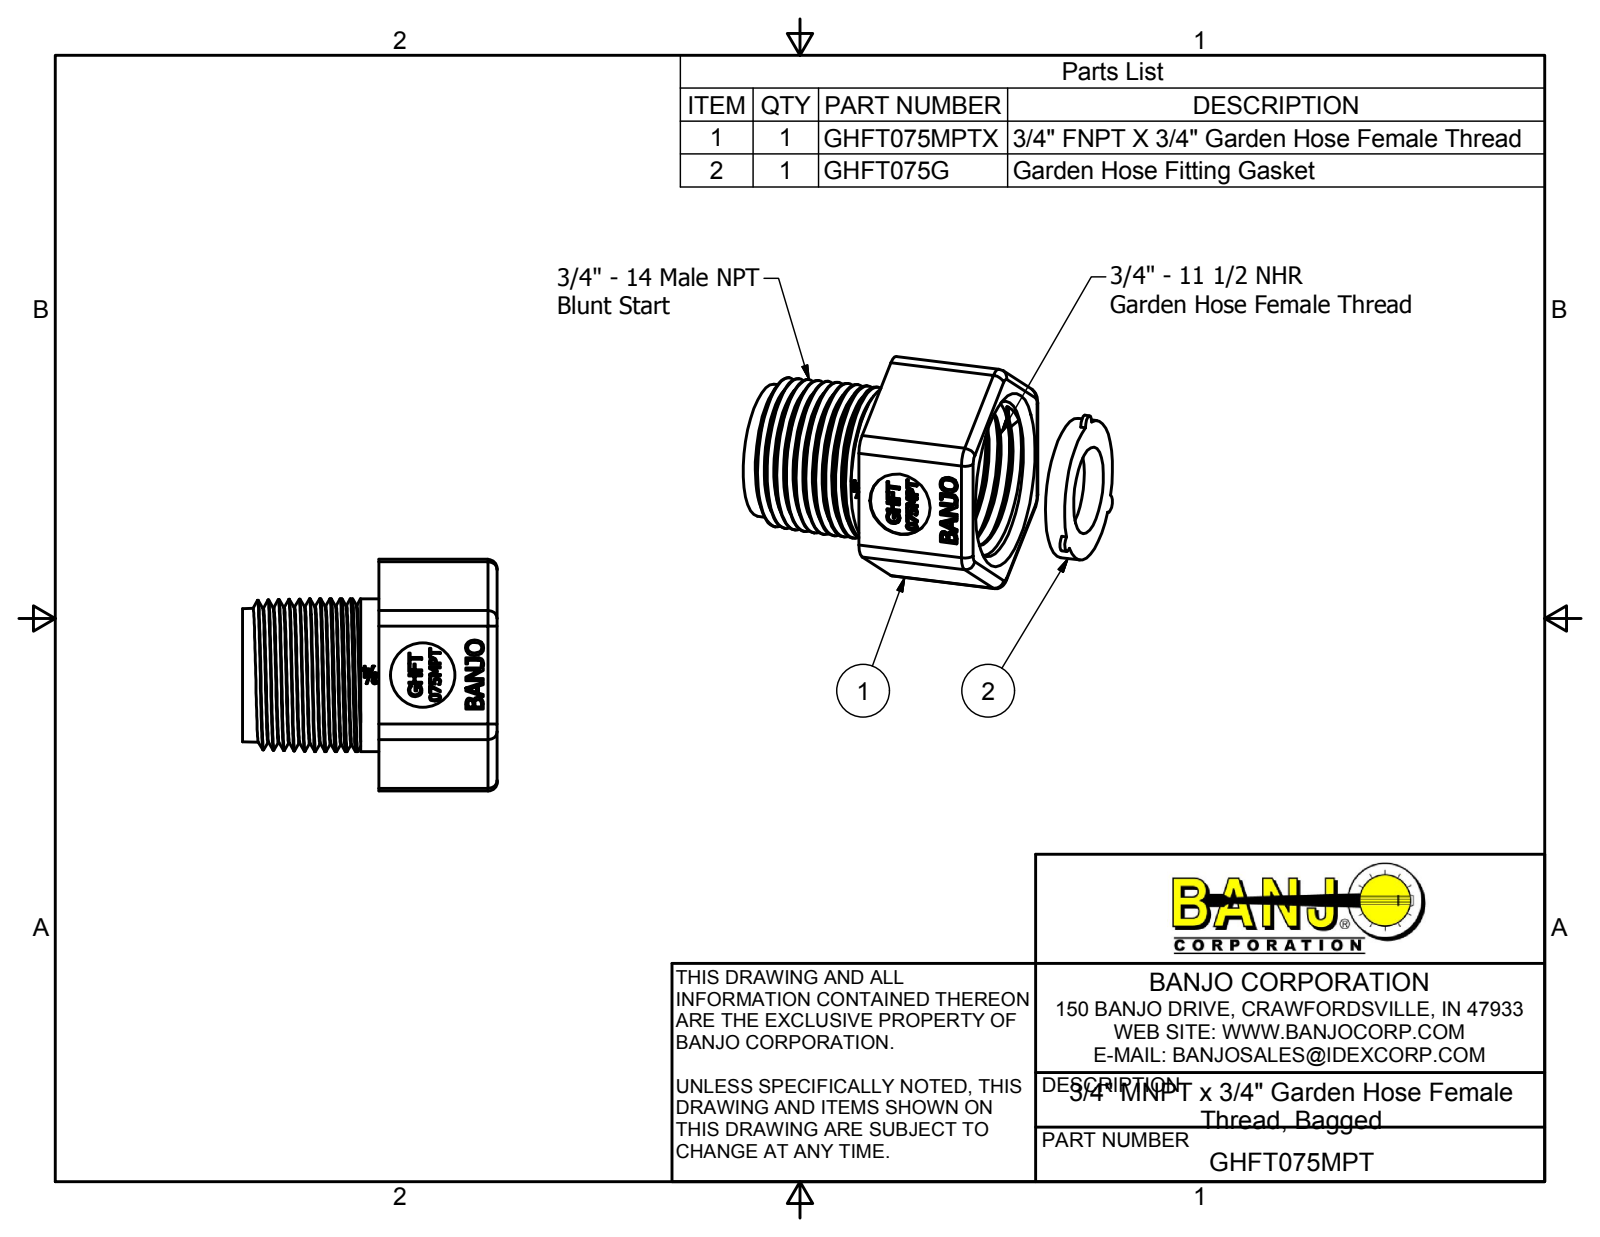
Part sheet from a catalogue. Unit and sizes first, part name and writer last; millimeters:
Units: millimetres
Overall size (bounding box): 44.45 × 40.4 × 35.84
Round holes (diameter × count): ⌀11.18 ×1, ⌀15.24 ×1, ⌀19.81 ×1, ⌀23.96 ×1, ⌀27.3 ×1
Round bosses / shafts (diameter × count): ⌀26.67 ×1, ⌀24.51 ×1
Partial cylindrical surfaces — rounded edges, fillets, slot ends (radius × count): R1.59 ×6, R3.17 ×6, R1.52 ×3, R7.2 ×1, R8.5 ×1, R13.59 ×1
Main face-to-face distances: 35.84, 7.18, 10.73, 3.55, 20.64, 9.91, 13.46, 23.81, 30.99, 34.54
Volume: 19 078 mm³ · Surface area: 11 753 mm²
Bodies: 2 solids, 372 faces (202 planar, 36 cylindrical, 134 other)
Part name (STEP PRODUCT): GHFT075MPTX; GHFT075G; GHFT075MPT
STEP written by: Autodesk Inventor 2015 (AUTOMOTIVE_DESIGN)
